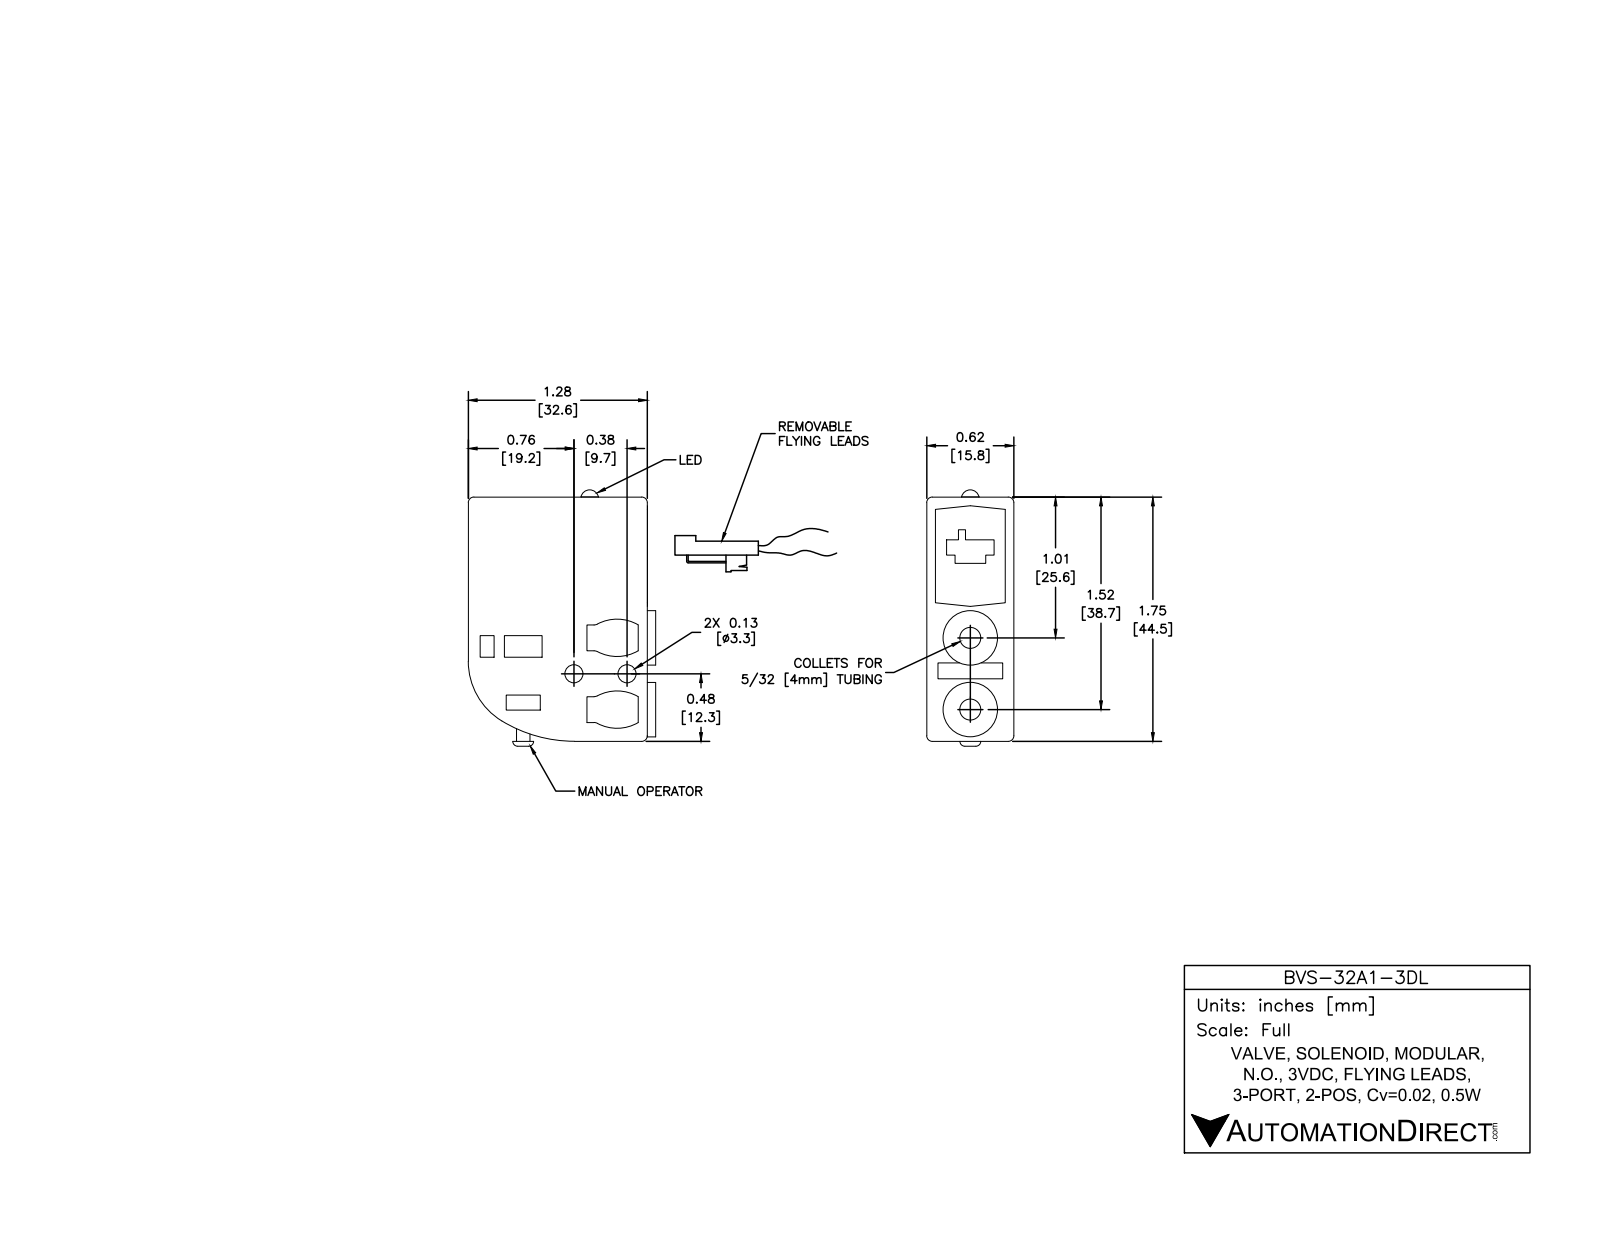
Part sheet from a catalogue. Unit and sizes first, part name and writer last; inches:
Units: inches
Overall size (bounding box): 1.84 × 1.788 × 0.62
Round holes (diameter × count): ⌀0.13 ×2, ⌀0.15 ×2, ⌀0.25 ×2, ⌀0.05 ×1
Round bosses / shafts (diameter × count): ⌀0.06 ×6, ⌀0.39 ×2, ⌀0.1 ×1
Partial cylindrical surfaces — rounded edges, fillets, slot ends (radius × count): R0.05 ×4, R0.3 ×4, R0.04 ×3, R0.5 ×1, R1 ×1
Main face-to-face distances: 0.62, 0.1, 1.29, 0.52, 1.291, 1.75, 1, 0.15, 0.06, 1.35
Hole centre spacings: 0.06, 0.38, 0.45, 0.51
Volume: 1.259 in³ · Surface area: 10.37 in²
Bodies: 1 solid, 149 faces (83 planar, 54 cylindrical, 12 other)
Part name (STEP PRODUCT): BVS-32A1-3DL
STEP written by: SolidWorks 2016 (AUTOMOTIVE_DESIGN)
